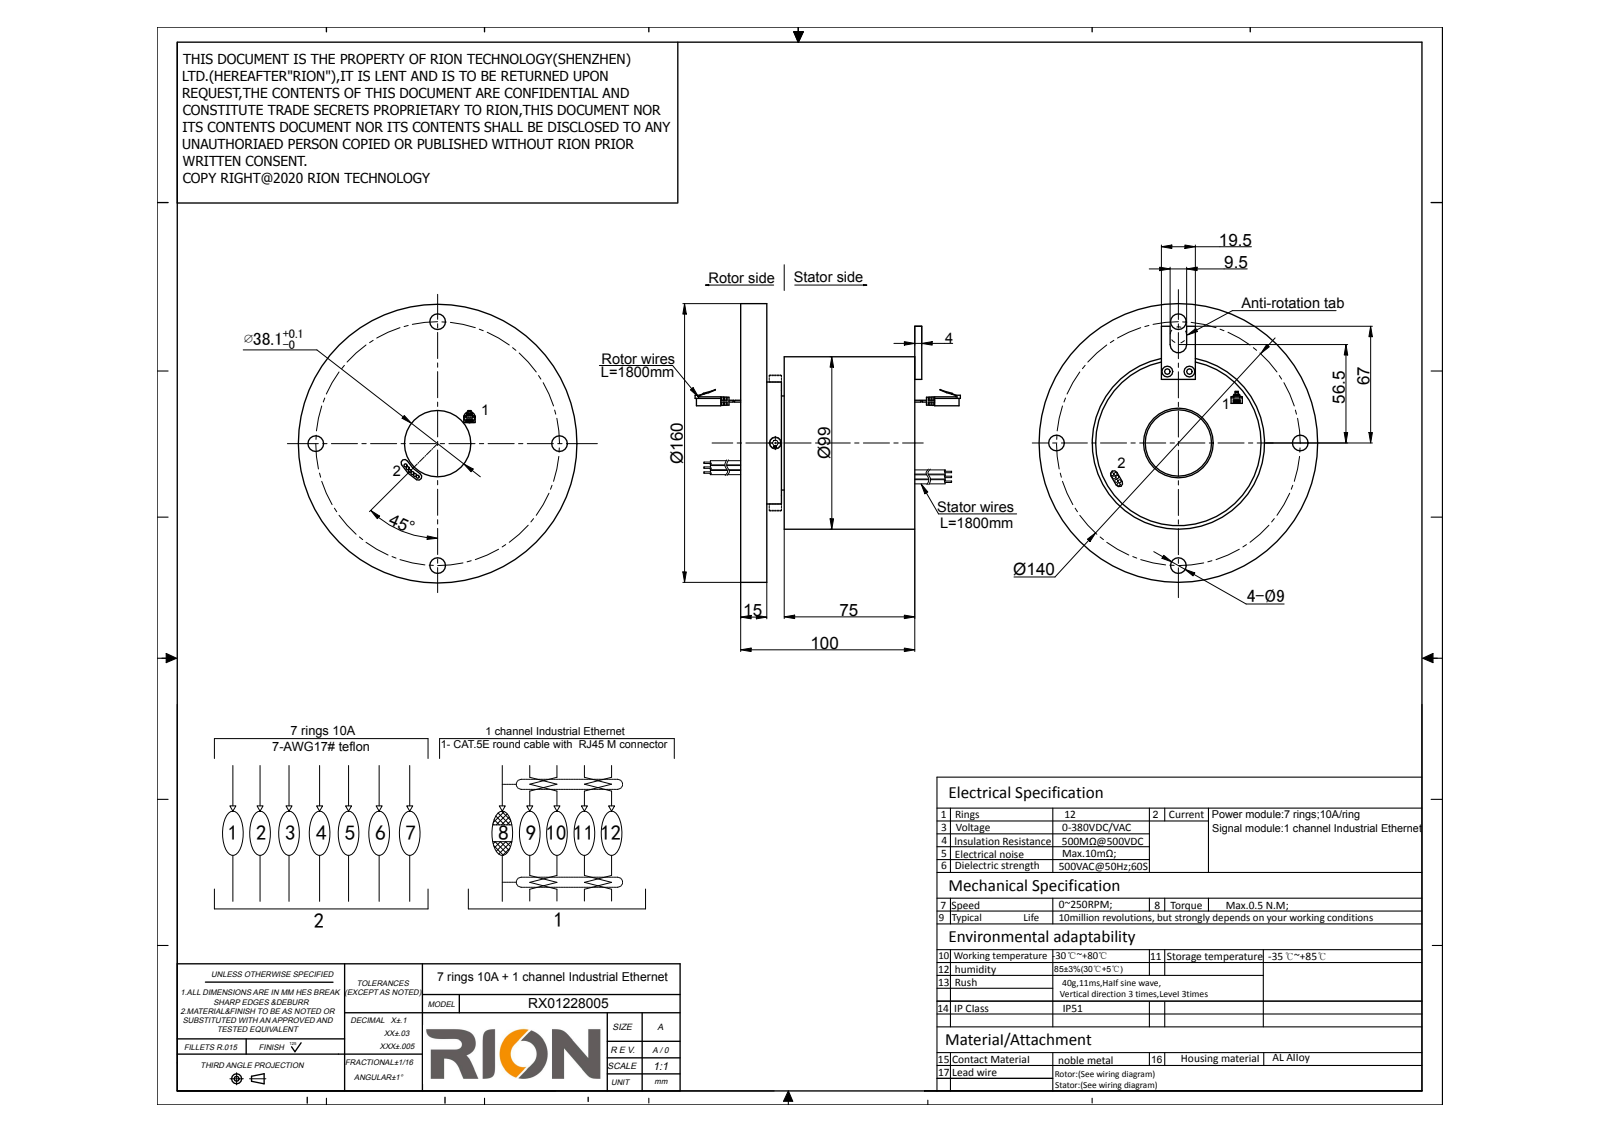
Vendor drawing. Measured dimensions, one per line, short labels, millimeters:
name: RX01228005
written by: SolidWorks 2014 (CONFIG_CONTROL_DESIGN)
unit: mm
bodies: 1 solid, 114 faces (41 planar, 69 cylindrical, 4 other)
size: 160 × 160 × 140
volume: 799 701 mm³; area: 100 045 mm²
holes: 4× ⌀9, 2× ⌀3.2, 1× ⌀6.5, 1× ⌀7, 1× ⌀38.1, 1× ⌀95.4
bosses: 13× ⌀1.8, 1× ⌀160, 1× ⌀99, 1× ⌀95, 1× ⌀70, 1× ⌀54, 1× ⌀6.5
rounds: 4× R2, 1× R4.75, 1× R20, 1× R24
face distances: 15, 100, 85, 25, 10, 75, 23.4, 8.4, 1.6, 76.6
hole spacings: 70, 98.99, 29.69, 41.49, 75.71, 86.66, 111.18, 140
